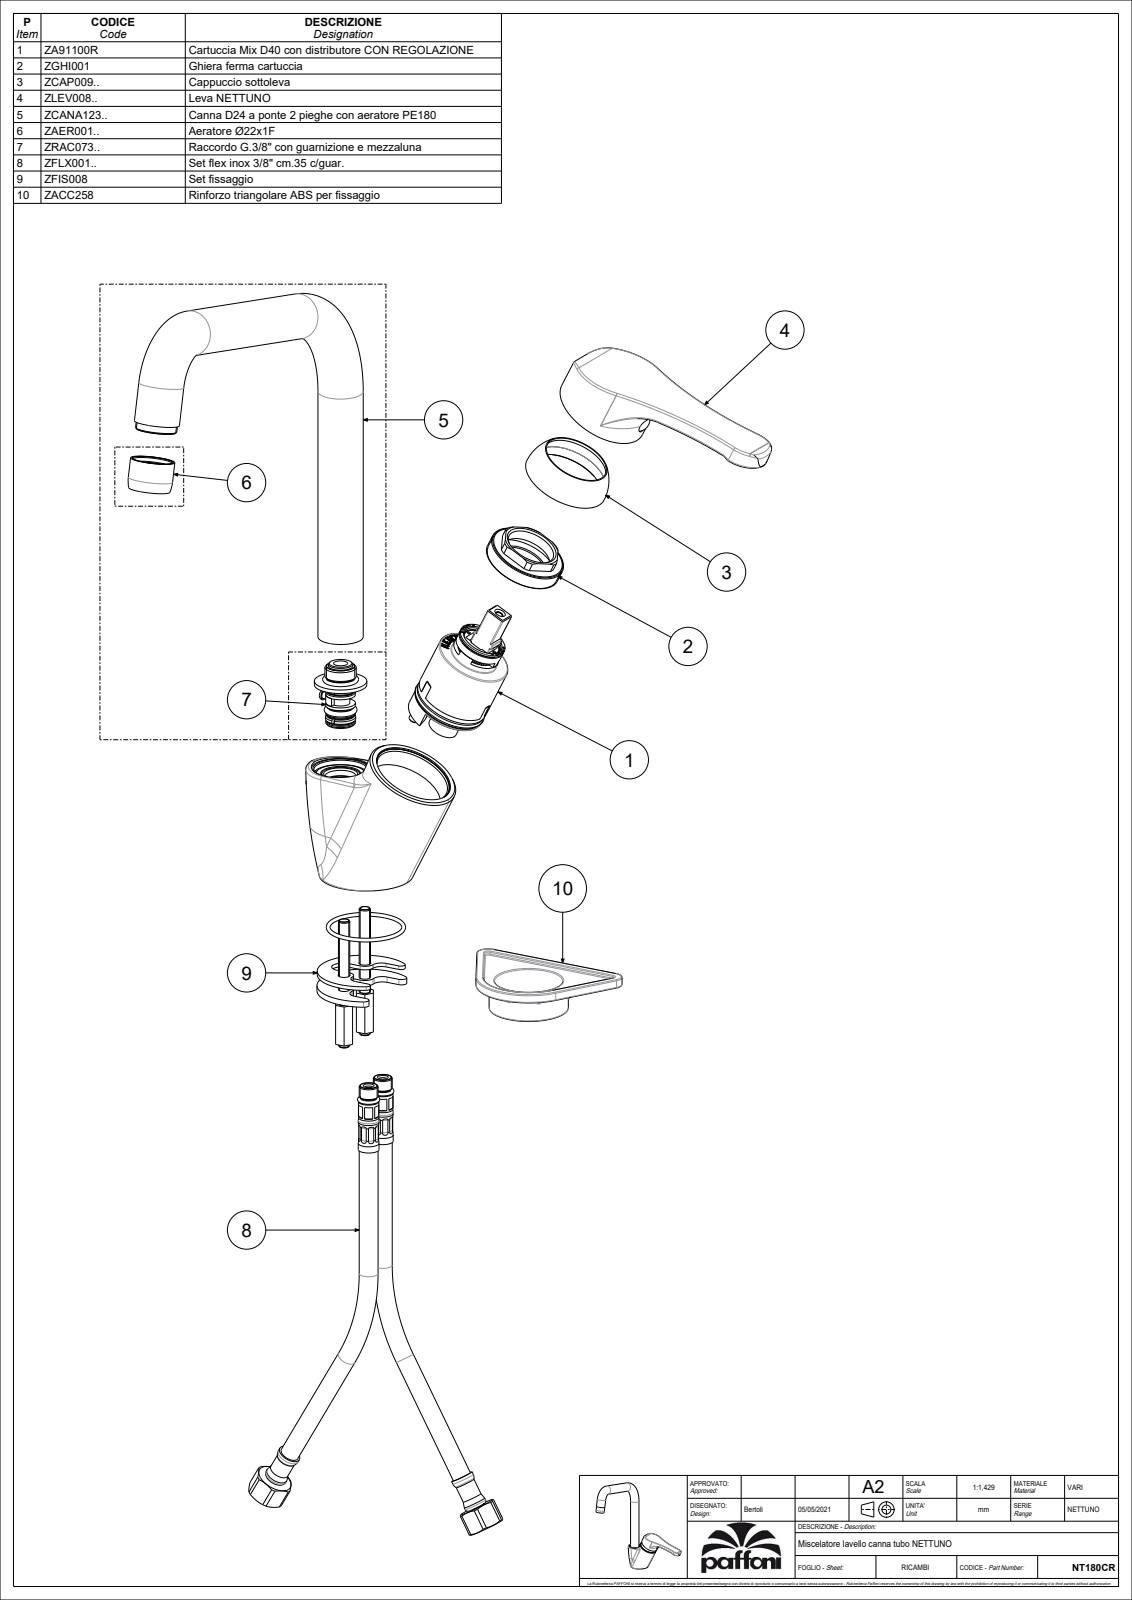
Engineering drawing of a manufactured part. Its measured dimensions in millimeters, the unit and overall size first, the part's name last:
Units: millimetres
Overall size (bounding box): 290.6 × 234.05 × 167.28
Round holes (diameter × count): ⌀8 ×5, ⌀21 ×4, ⌀5 ×3, ⌀11 ×3, ⌀6 ×2, ⌀9 ×2, ⌀12 ×2, ⌀16 ×2, ⌀17 ×2, ⌀3.3 ×1, ⌀4 ×1, ⌀4.5 ×1
Round bosses / shafts (diameter × count): ⌀24 ×3, ⌀15.9 ×2, ⌀9.4 ×2, ⌀50 ×1, ⌀39.5 ×1, ⌀39.2 ×1, ⌀38.8 ×1, ⌀37 ×1
Partial cylindrical surfaces — rounded edges, fillets, slot ends (radius × count): R0.5 ×51, R0.2 ×24, R1.5 ×6, R1 ×5, R0.3 ×4, R2 ×4, R5.5 ×2, R7.5 ×2
Main face-to-face distances: 1, 3, 8, 5, 2.5, 1.5, 0.5, 4, 10, 13
Hole centre spacings: 2, 8.6, 8.72, 9.9, 9.92, 10.04, 12.78, 13.04
Volume: 216 710 mm³ · Surface area: 134 064 mm²
Bodies: 2 solids, 2771 faces (2000 planar, 413 cylindrical, 358 other)
Part name (STEP PRODUCT): NT180CR
STEP written by: CREO PARAMETRIC BY PTC INC, 2020044 (CONFIG_CONTROL_DESIGN)
